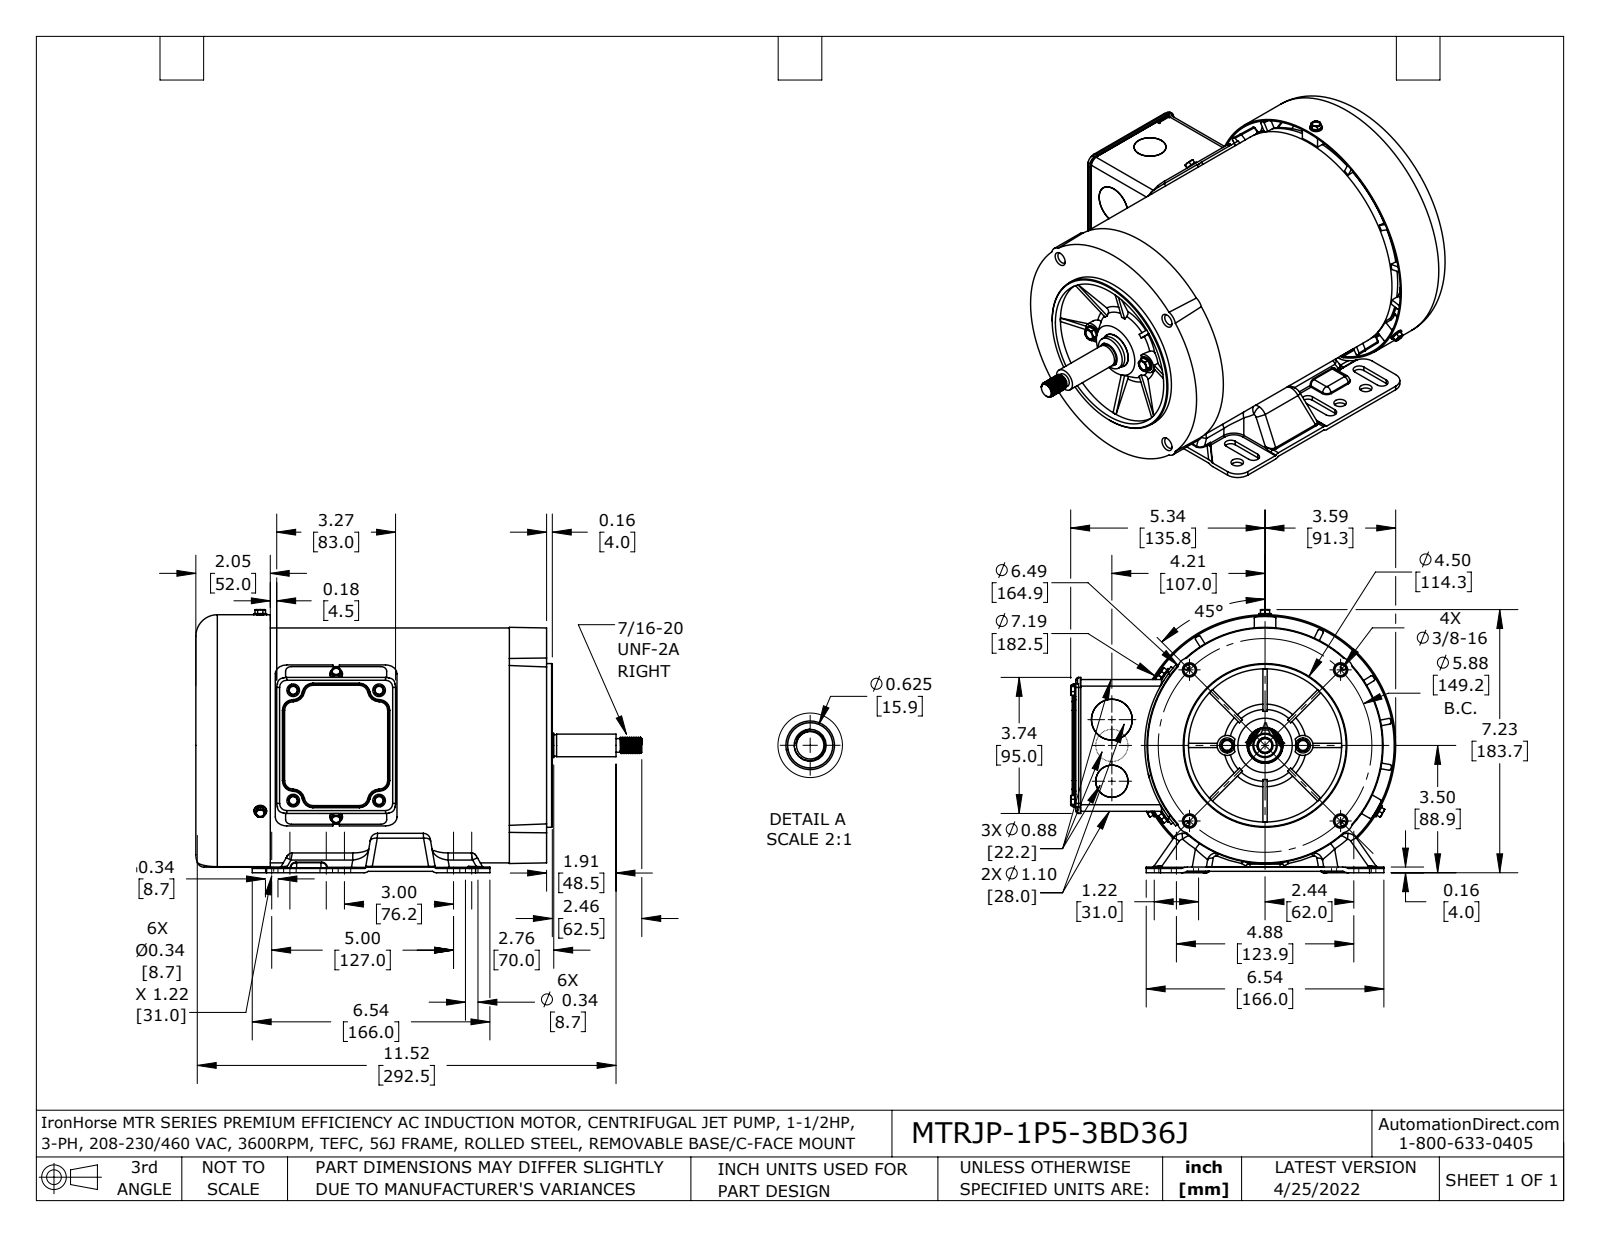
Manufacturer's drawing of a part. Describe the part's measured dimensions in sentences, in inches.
The part is named "MTRJP-1P5-3BD36J redcmb1 coord fxt". Its 3-D file was written by "SolidWorks 2021 (AUTOMOTIVE_DESIGN)". It is 24 solids with 2699 faces: 648 planar, 879 cylindrical and 1172 other. Overall it measures 12.264 by 8.938 by 7.234 inches. Its volume is 46.27 cubic inches and its surface area 890.9 square inches. Round holes: 10 of diameter 0.197, 9 of diameter 0.219, 8 of diameter 0.276, 7 of diameter 0.136, 6 of diameter 0.217, 6 of diameter 0.328, 6 of diameter 0.344, 4 of diameter 0.15, 4 of diameter 0.177, 4 of diameter 0.313, 2 of diameter 0.134, 2 of diameter 0.273. Round bosses or shafts: 9 of diameter 0.164, 8 of diameter 0.348, 6 of diameter 0.236, 2 of diameter 0.414, 2 of diameter 0.19, 1 of diameter 7.185, 1 of diameter 4.5, 1 of diameter 0.945. Partial cylindrical surfaces (rounded edges, fillets, slot ends): 109 of radius 0.118, 65 of radius 0.039, 32 of radius 0.157, 30 of radius 0.02, 26 of radius 0.138, 18 of radius 0.079, 18 of radius 0.276, 12 of radius 0.172. The main face-to-face distances are 0.039, 0.118, 0.063, 0.157, 9.646, 9.606, 0.079, 3.559, 3.087, 0.047. The hole center spacings are 4.221, 3.031, 0.094, 2.32, 2.409, 2.937, 3.748, 3.841.
